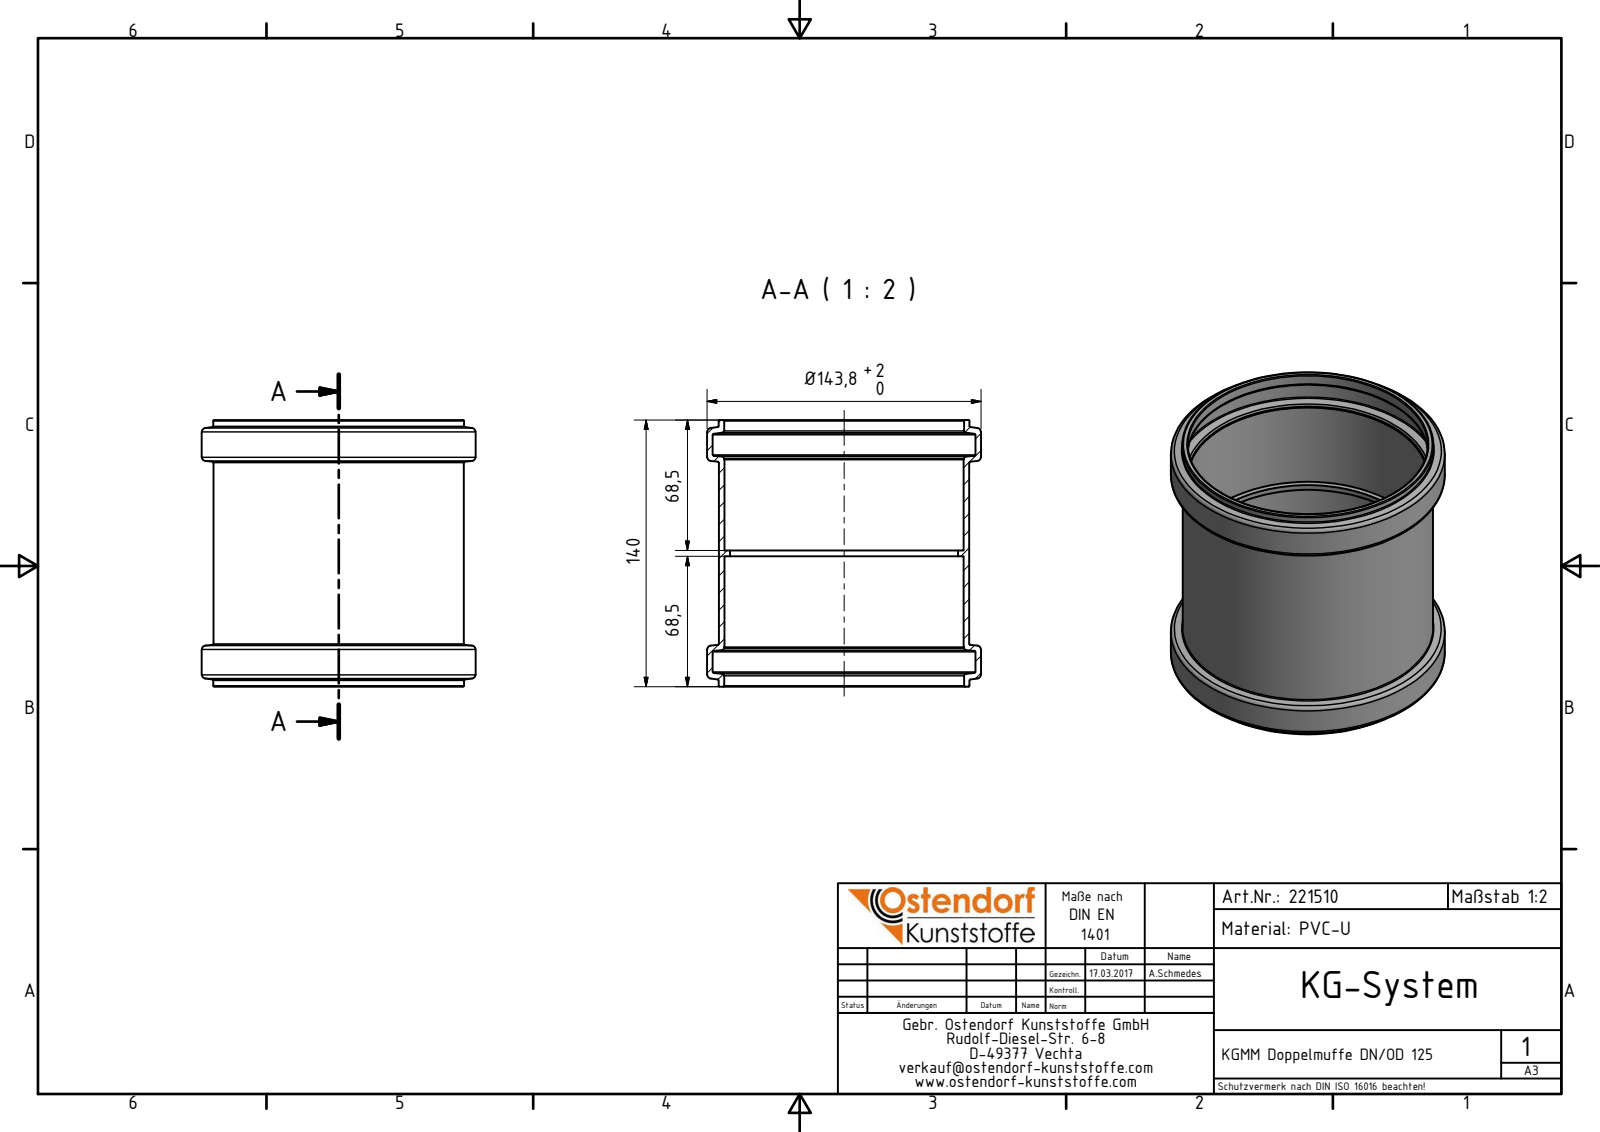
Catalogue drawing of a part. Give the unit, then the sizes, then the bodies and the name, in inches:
Units: inches
Overall size (bounding box): 5.661 × 5.661 × 5.512
Round holes (diameter × count): ⌀4.713 ×1, ⌀4.949 ×1, ⌀4.961 ×1, ⌀5.433 ×1
Round bosses / shafts (diameter × count): ⌀5.661 ×1, ⌀5.189 ×1, ⌀5.177 ×1
Main face-to-face distances: 2.697, 2.815, 0.118, 5.512, 0.815, 4.697, 1.882, 2, 3.882
Volume: 12.06 in³ · Surface area: 210.7 in²
Bodies: 1 solid, 48 faces (6 planar, 14 cylindrical, 28 other)
Part name (STEP PRODUCT): 221510 KGMM Doppelmuffe DN_OD 125
STEP written by: Autodesk Inventor 2016 (AUTOMOTIVE_DESIGN)
